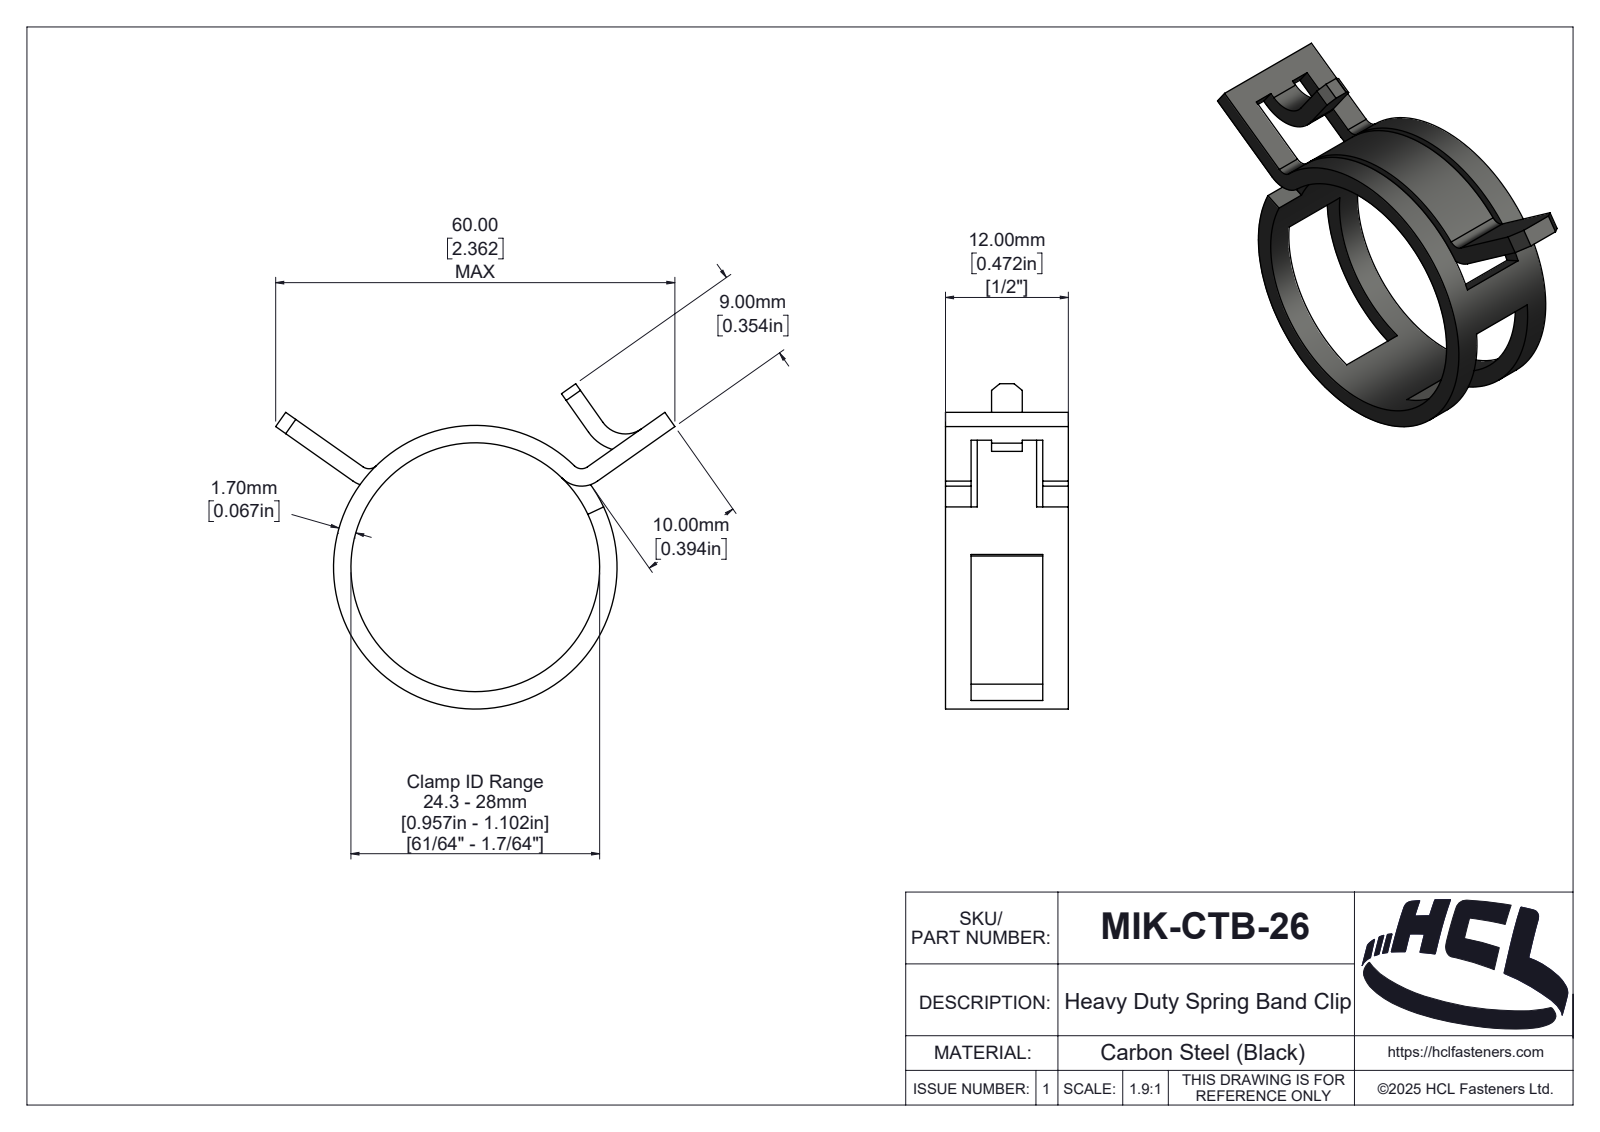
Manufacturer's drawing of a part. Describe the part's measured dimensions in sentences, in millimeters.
The part is named "MIK-CTB-26". Its 3-D file was written by "SolidWorks 2025 (AUTOMOTIVE_DESIGN)". It is 1 solid with 149 faces: 36 planar, 64 cylindrical and 49 other. Overall it measures 39 by 31.77 by 12 millimeters. Its volume is 1 409 cubic millimeters and its surface area 2 469 square millimeters. Round holes: 1 of diameter 24.3. Round bosses or shafts: 1 of diameter 27.7. Partial cylindrical surfaces (rounded edges, fillets, slot ends): 3 of radius 2.7, 2 of radius 1, 1 of radius 0.33, 1 of radius 1.35, 1 of radius 1.68, 1 of radius 1.77, 1 of radius 2.14, 1 of radius 3.02. The main face-to-face distances are 2.5, 9.5, 12, 1.7, 3.1, 8.9, 0.6, 6.4, 7, 5.8.
